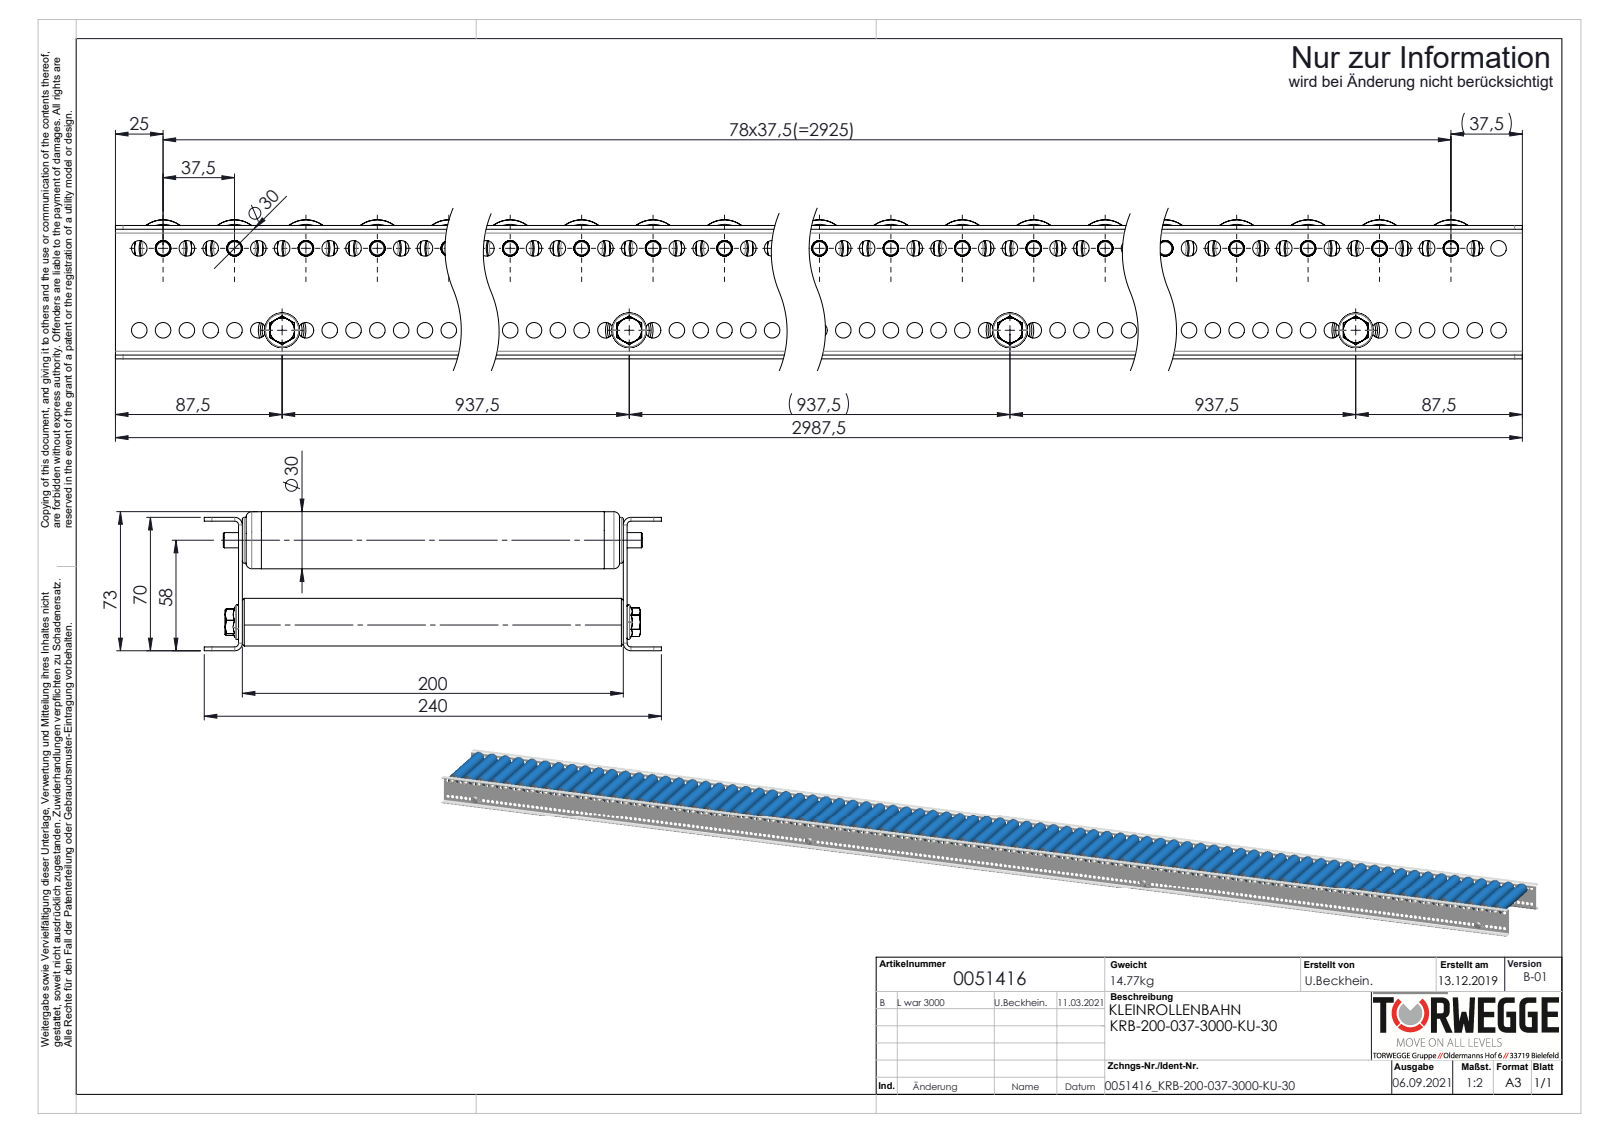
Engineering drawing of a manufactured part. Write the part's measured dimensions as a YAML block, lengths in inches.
part_name: "0051416; KUT50-30x1,8-KB-A8-FA_KFG_0034504TWG_KUT50-30x1,8-KB-A8-FA-EL=200; 0017013_Tragrollenrohr-Ø30x1,8KU_KFG_L=180; 0039778-Achse-ST-Ø08-KFG_AL220-G-FA (+4 more)"
step_written_by: "SolidWorks 2020 (AUTOMOTIVE_DESIGN)"
units: inches
bodies: {solids: 180, faces: 18686, planar: 5734, cylindrical: 7056, other: 5896}
overall_size: [117.618, 9.449, 2.874]
volume: 271.4
surface_area: 8151
round_holes:
  - {diameter: 0.323, count: 476}
  - {diameter: 0.319, count: 79}
  - {diameter: 0.89, count: 79}
  - {diameter: 0.992, count: 79}
  - {diameter: 0.268, count: 4}
  - {diameter: 0.827, count: 4}
round_bosses_or_shafts:
  - {diameter: 0.315, count: 83}
  - {diameter: 1.181, count: 79}
  - {diameter: 1.177, count: 79}
  - {diameter: 1.043, count: 79}
  - {diameter: 1.039, count: 79}
  - {diameter: 0.945, count: 79}
  - {diameter: 0.984, count: 4}
partial_cylinders:
  - {radius: 0.199, count: 79}
  - {radius: 0.157, count: 8}
  - {radius: 0.079, count: 4}
face_to_face_distances: [0.079, 7.953, 2.677, 7.874, 8.031, 2.756, 2.598, 0.394, 7.48, 0.472]
hole_center_spacings: [0.492, 0.984, 1.476, 1.969, 2.461, 2.953, 3.445, 3.937]
